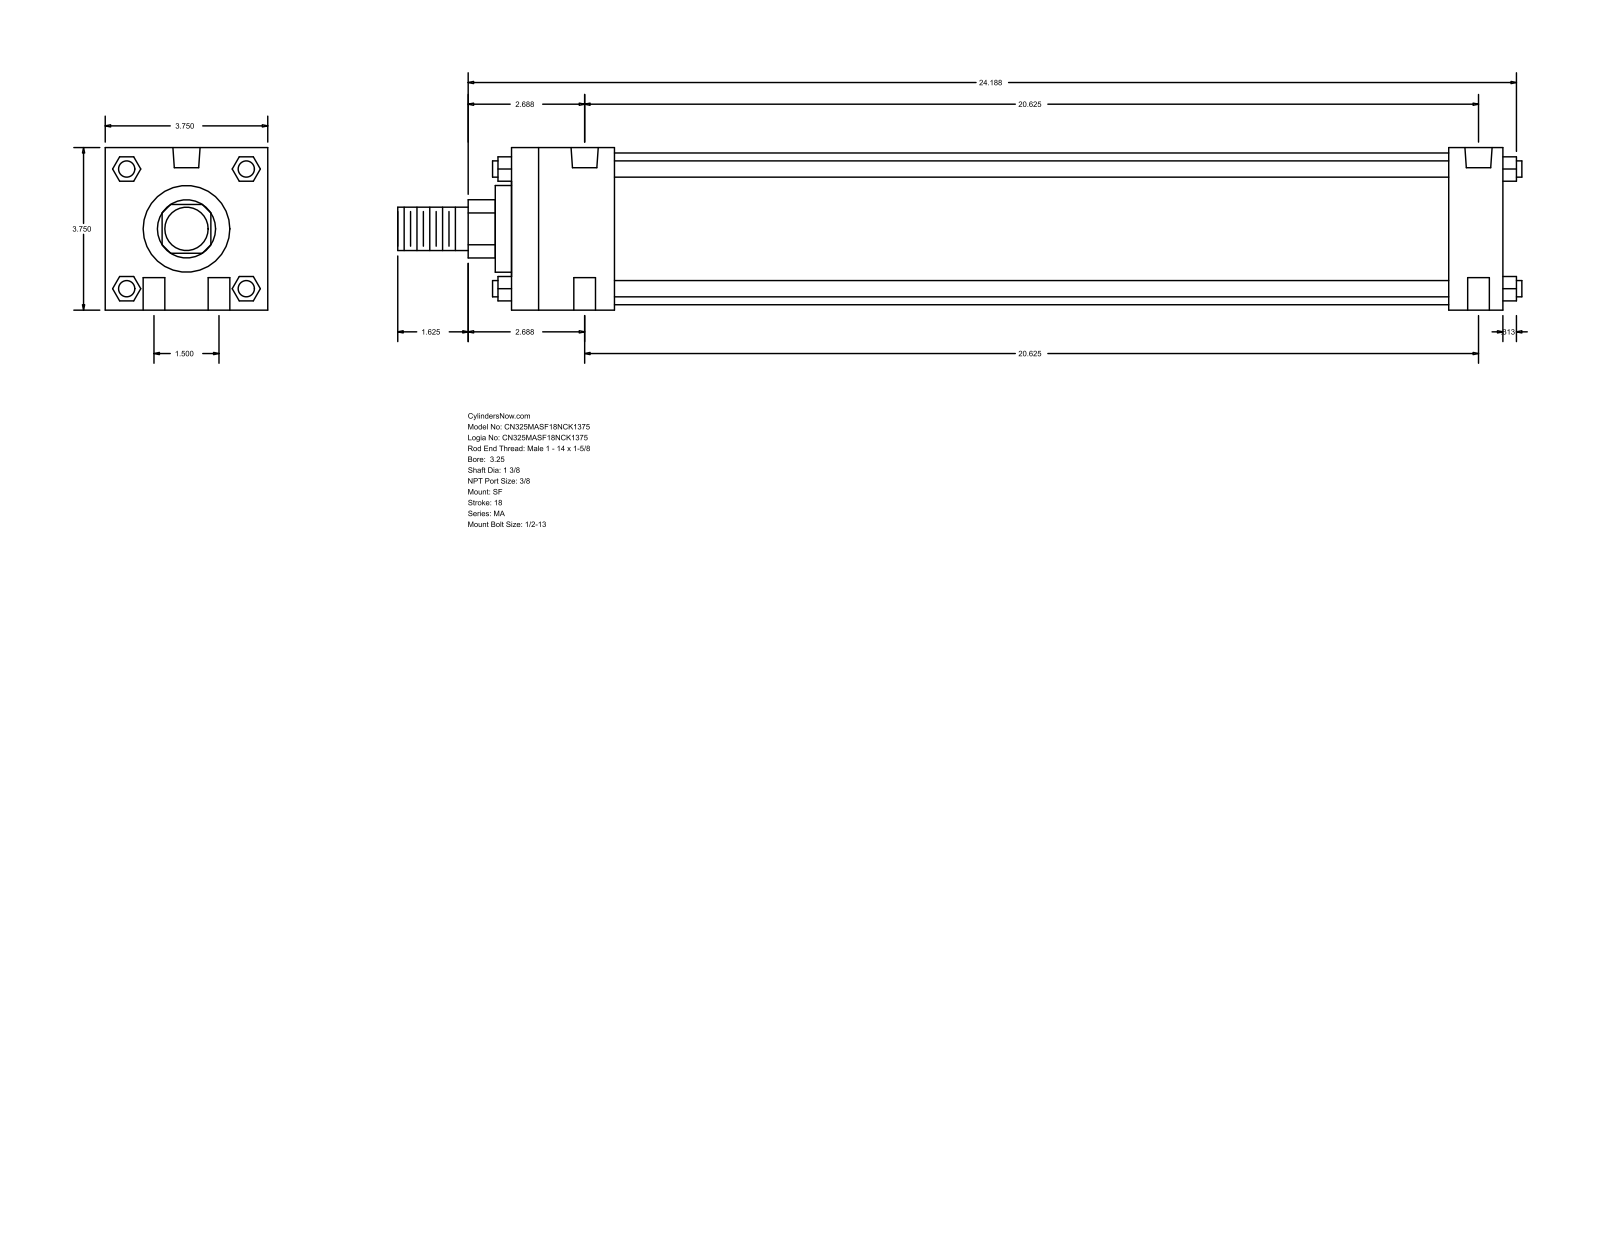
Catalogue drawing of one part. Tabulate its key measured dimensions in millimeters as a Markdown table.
| quantity | value |
| --- | --- |
| part name | MA_SF__0325_1.375 |
| STEP written by | GSSL Pune (CONFIG_CONTROL_DESIGN) |
| units | millimeters |
| bodies | 0 solids, 124 faces (94 planar, 30 cylindrical, 0 other) |
| overall size | 658.81 × 95.25 × 95.25 |
| round holes (diameter × count) | 12.7 × 4, 11.11 × 2, 15.93 × 2 |
| round bosses / shafts (diameter × count) | 9.53 × 4, 88.9 × 1, 50.8 × 1, 34.92 × 1, 25.4 × 1 |
| partial cylindrical surfaces (radius × count) | 17.06 × 1 |
| main face-to-face distances | 95.24, 581.02, 549.27, 31.75, 60.32, 488.95, 520.7, 9.52, 69.84, 558.79 |
| hole center spacings | 19.05, 524.23, 523.88, 38.1, 525.26, 514.35 |
